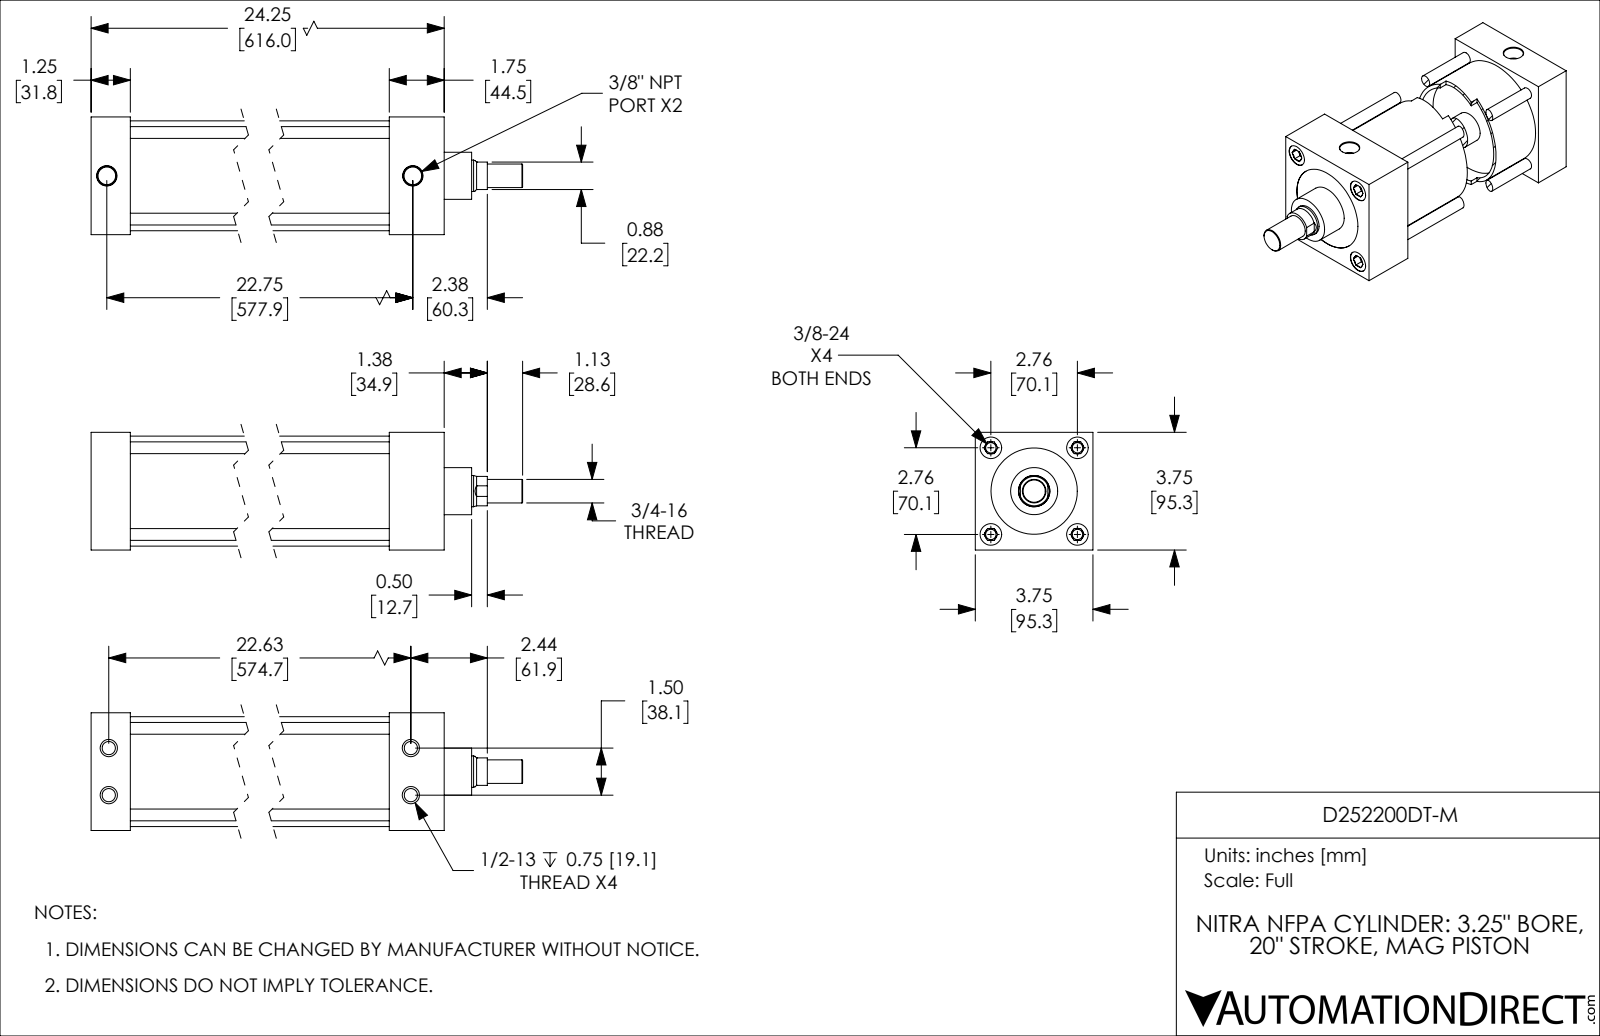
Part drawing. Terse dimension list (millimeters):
name: D252200DT-M_PISTON_KK1; D252200DT-M; D252200DT-M_BODY
written by: SolidWorks 2019 (CONFIG_CONTROL_DESIGN)
unit: mm
bodies: 2 solids, 198 faces (58 planar, 62 cylindrical, 78 other)
size: 679.5 × 95.3 × 95.3
volume: 1 737 000 mm³; area: 504 900 mm²
holes: 4× ⌀8.4, 4× ⌀10.7, 4× ⌀17.4, 2× ⌀14.3, 1× ⌀25.4, 1× ⌀69.9, 1× ⌀82.6
bosses: 4× ⌀9.5, 1× ⌀88.9, 1× ⌀82.5, 1× ⌀38.1, 1× ⌀25.4, 1× ⌀19.1
rounds: 1× R11.9
face distances: 31.8, 95.3, 571.5, 539.8, 63.5, 508, 616, 584.2, 552.5, 44.5
hole spacings: 19.1, 49.6, 70.1, 576.6, 38.1, 99.1, 574.7, 575.9
